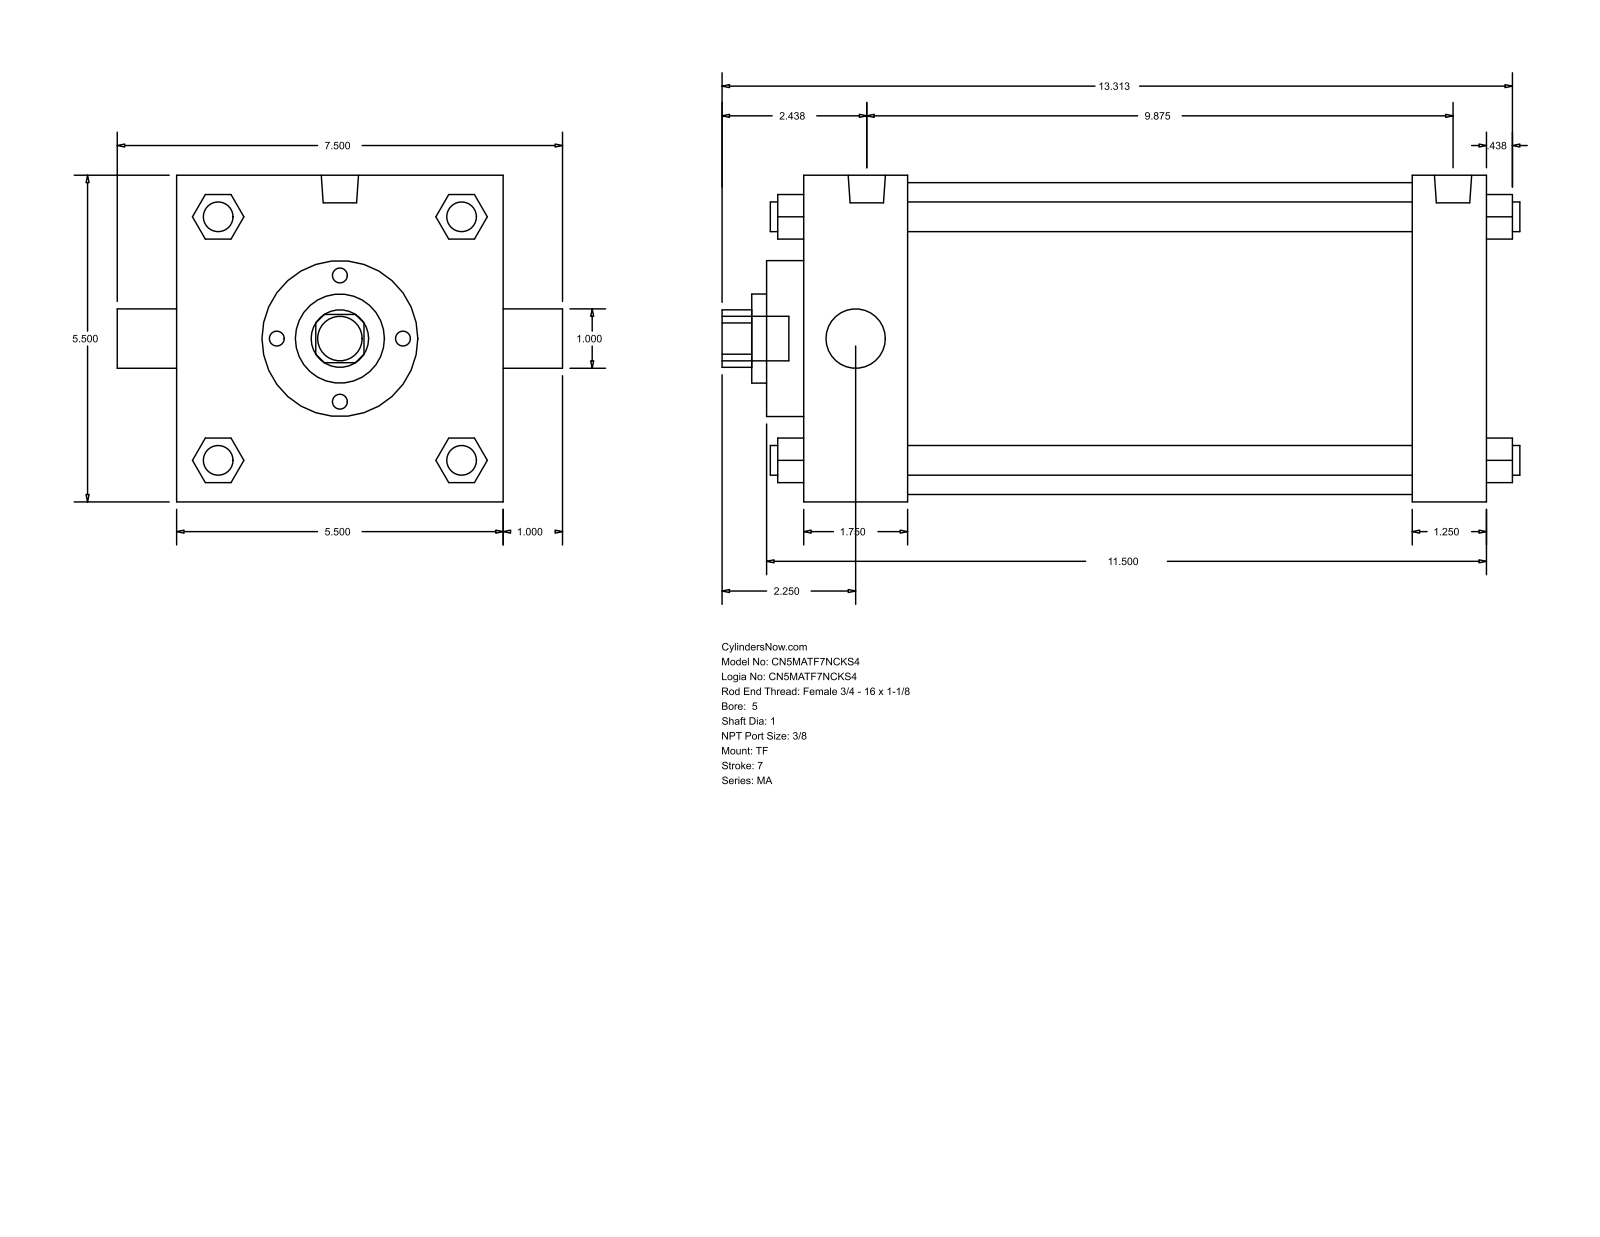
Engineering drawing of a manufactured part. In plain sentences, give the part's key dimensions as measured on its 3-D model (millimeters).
The part is named "MA_TF__0500_1". Its 3-D file was written by "GSSL Pune (CONFIG_CONTROL_DESIGN)". It is 0 solids with 122 faces: 93 planar, 29 cylindrical and 0 other. Overall it measures 341.31 by 190.5 by 139.7 millimeters. Round holes: 2 of diameter 25.4, 1 of diameter 38.1, 1 of diameter 66.67, 1 of diameter 133.35. Round bosses or shafts: 4 of diameter 12.7, 3 of diameter 11.11, 2 of diameter 15.93, 1 of diameter 19.05. Partial cylindrical surfaces (rounded edges, fillets, slot ends): 1 of radius 12.29. The main face-to-face distances are 139.7, 292.1, 260.35, 31.75, 44.46, 215.89, 247.64, 15.87, 60.33, 276.22.
